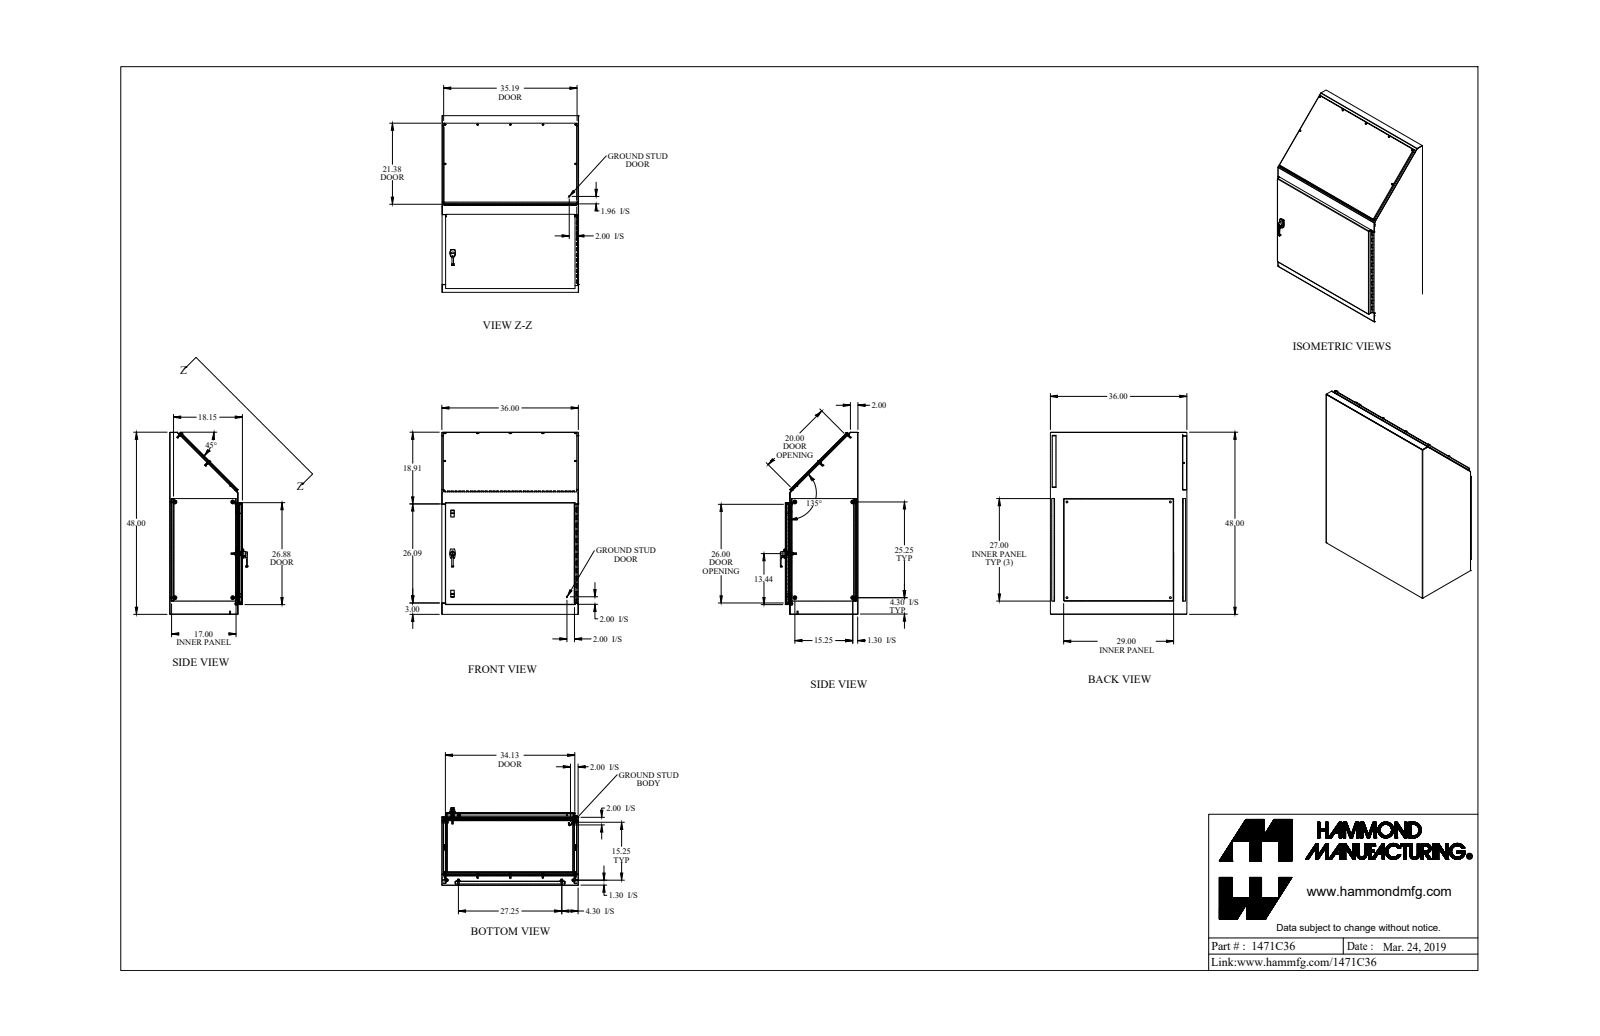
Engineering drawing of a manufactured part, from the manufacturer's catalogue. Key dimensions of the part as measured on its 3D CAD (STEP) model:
Part name (STEP PRODUCT): 1471C36_Default
STEP written by: SolidWorks 2019 (CONFIG_CONTROL_DESIGN)
Units: inches
Bodies: 113 solids, 2579 faces (1268 planar, 1048 cylindrical, 263 other)
Overall size (bounding box): 48 × 36 × 20.465
Volume: 685.6 in³ · Surface area: 17 247 in²
Round holes (diameter × count): ⌀0.307 ×13, ⌀0.5 ×12, ⌀0.25 ×8, ⌀0.159 ×7, ⌀0.445 ×6, ⌀0.218 ×4, ⌀0.445 ×4, ⌀0.187 ×3, ⌀0.127 ×2, ⌀0.156 ×2, ⌀0.189 ×2, ⌀0.195 ×2
Round bosses / shafts (diameter × count): ⌀1 ×11, ⌀0.65 ×10, ⌀0.375 ×10, ⌀0.33 ×10, ⌀0.402 ×9, ⌀0.18 ×9, ⌀0.39 ×7, ⌀0.275 ×6
Partial cylindrical surfaces — rounded edges, fillets, slot ends (radius × count): R0.036 ×23, R0.108 ×23, R0.125 ×19, R0.03 ×8, R0.05 ×8, R0.063 ×8, R0.16 ×7, R0.171 ×7
Main face-to-face distances: 0.072, 19.091, 0.095, 1.032, 1.104, 0.937, 1.009, 35.928, 19.019, 34.896
Hole centre spacings: 8.609, 25.25, 25.25, 29.498, 0.013, 37.15, 15.25, 17.219
